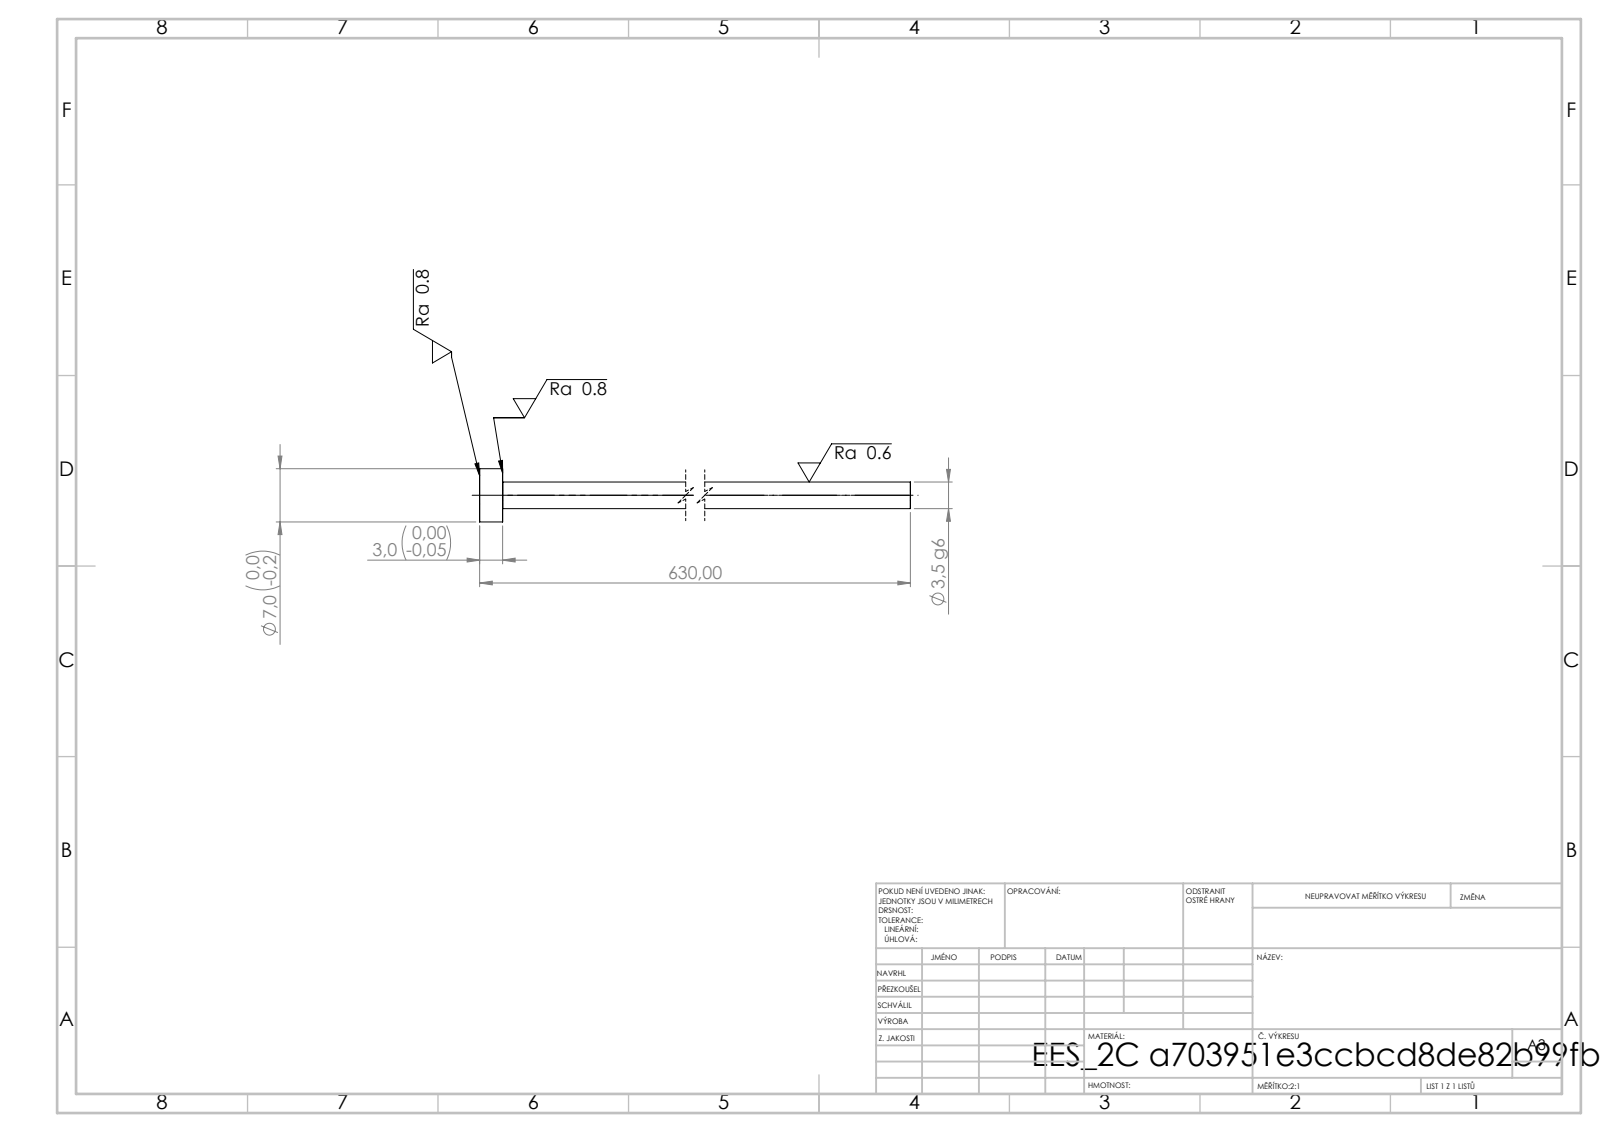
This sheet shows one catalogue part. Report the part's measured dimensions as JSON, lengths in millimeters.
{"step_written_by": "SolidWorks 2019 (CONFIG_CONTROL_DESIGN)", "units": "millimeters", "bodies": {"solids": 1, "faces": 7, "planar": 3, "cylindrical": 4, "other": 0}, "overall_size": [630, 7, 7], "volume_mm3": 6148, "surface_area_mm2": 7037, "round_bosses_or_shafts": [[7, 1], [3.5, 1]], "face_to_face_distances": [3, 630, 627]}
